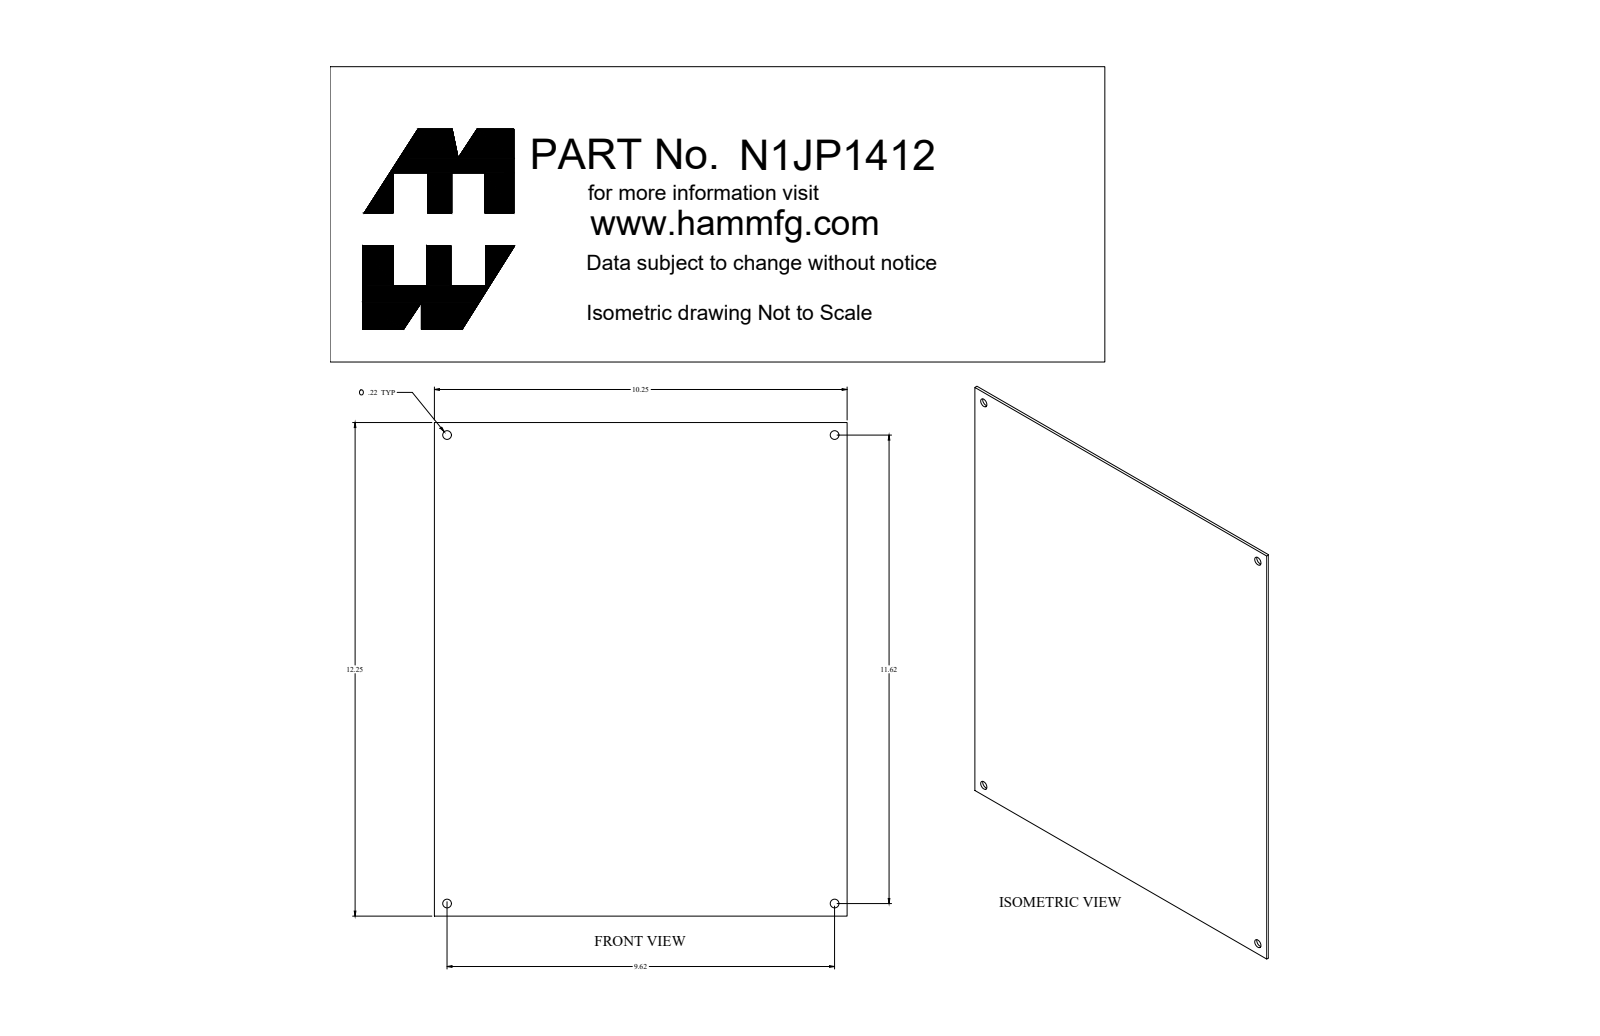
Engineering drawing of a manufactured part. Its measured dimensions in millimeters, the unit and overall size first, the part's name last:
Units: millimetres
Overall size (bounding box): 311.2 × 260.4 × 1.8
Round holes (diameter × count): ⌀6.7 ×2, ⌀6.7 ×2
Partial cylindrical surfaces — rounded edges, fillets, slot ends (radius × count): R3.2 ×4
Main face-to-face distances: 1.8, 260.4, 311.2
Hole centre spacings: 244.5, 295.3, 383.3
Volume: 147 900 mm³ · Surface area: 163 900 mm²
Bodies: 1 solid, 18 faces (6 planar, 12 cylindrical, 0 other)
Part name (STEP PRODUCT): N1JP1412
STEP written by: SolidWorks 2018 (AUTOMOTIVE_DESIGN)
